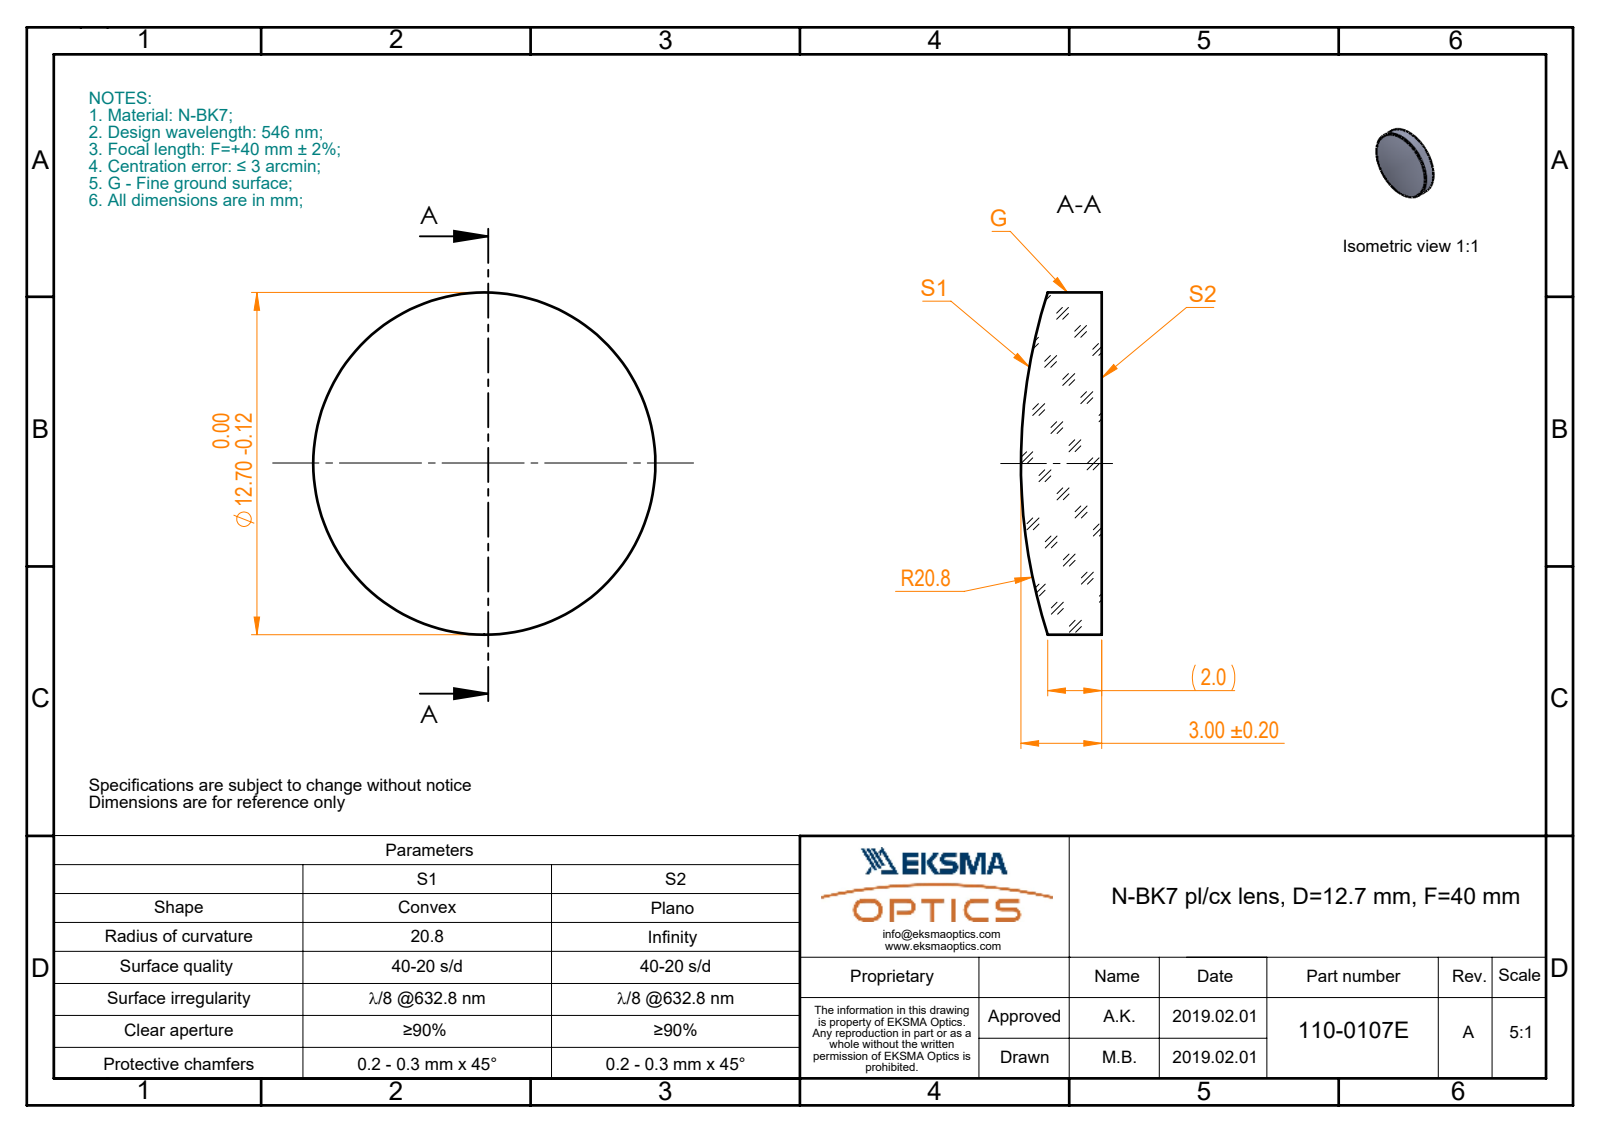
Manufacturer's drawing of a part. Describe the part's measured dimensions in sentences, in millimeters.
The part is named "110-0107E BK7 pl-cx 12.7 F40". Its 3-D file was written by "SolidWorks 2017 (CONFIG_CONTROL_DESIGN)". It is 1 solid with 5 faces: 1 planar, 2 cylindrical and 2 other. Overall it measures 12.7 by 12.7 by 3 millimeters. Its volume is 317 cubic millimeters and its surface area 336 square millimeters. Round bosses or shafts: 1 of diameter 12.7.
